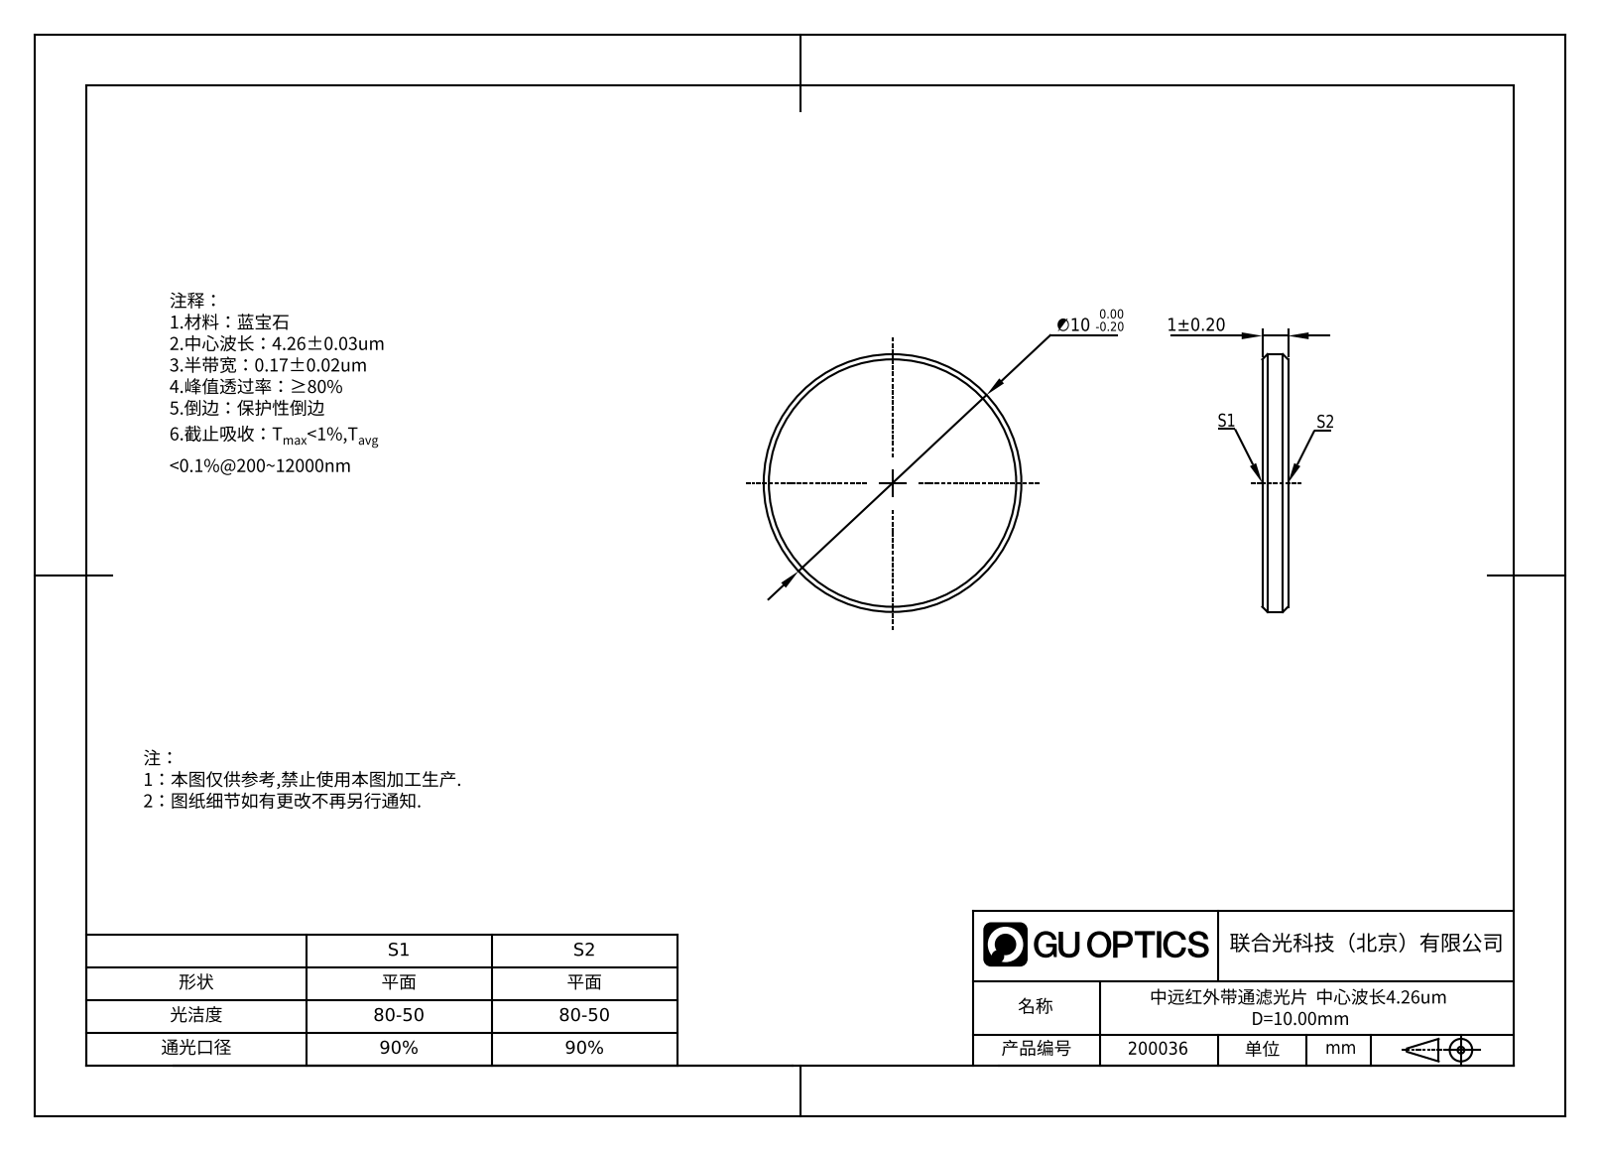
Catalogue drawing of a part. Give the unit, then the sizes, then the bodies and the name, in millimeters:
Units: millimetres
Overall size (bounding box): 10 × 10 × 1
Round bosses / shafts (diameter × count): ⌀10 ×1
Main face-to-face distances: 1
Volume: 77 mm³ · Surface area: 181 mm²
Bodies: 1 solid, 8 faces (2 planar, 2 cylindrical, 4 other)
Part name (STEP PRODUCT): GNIF-170-4260-D10
STEP written by: SolidWorks 2022 (AUTOMOTIVE_DESIGN)
